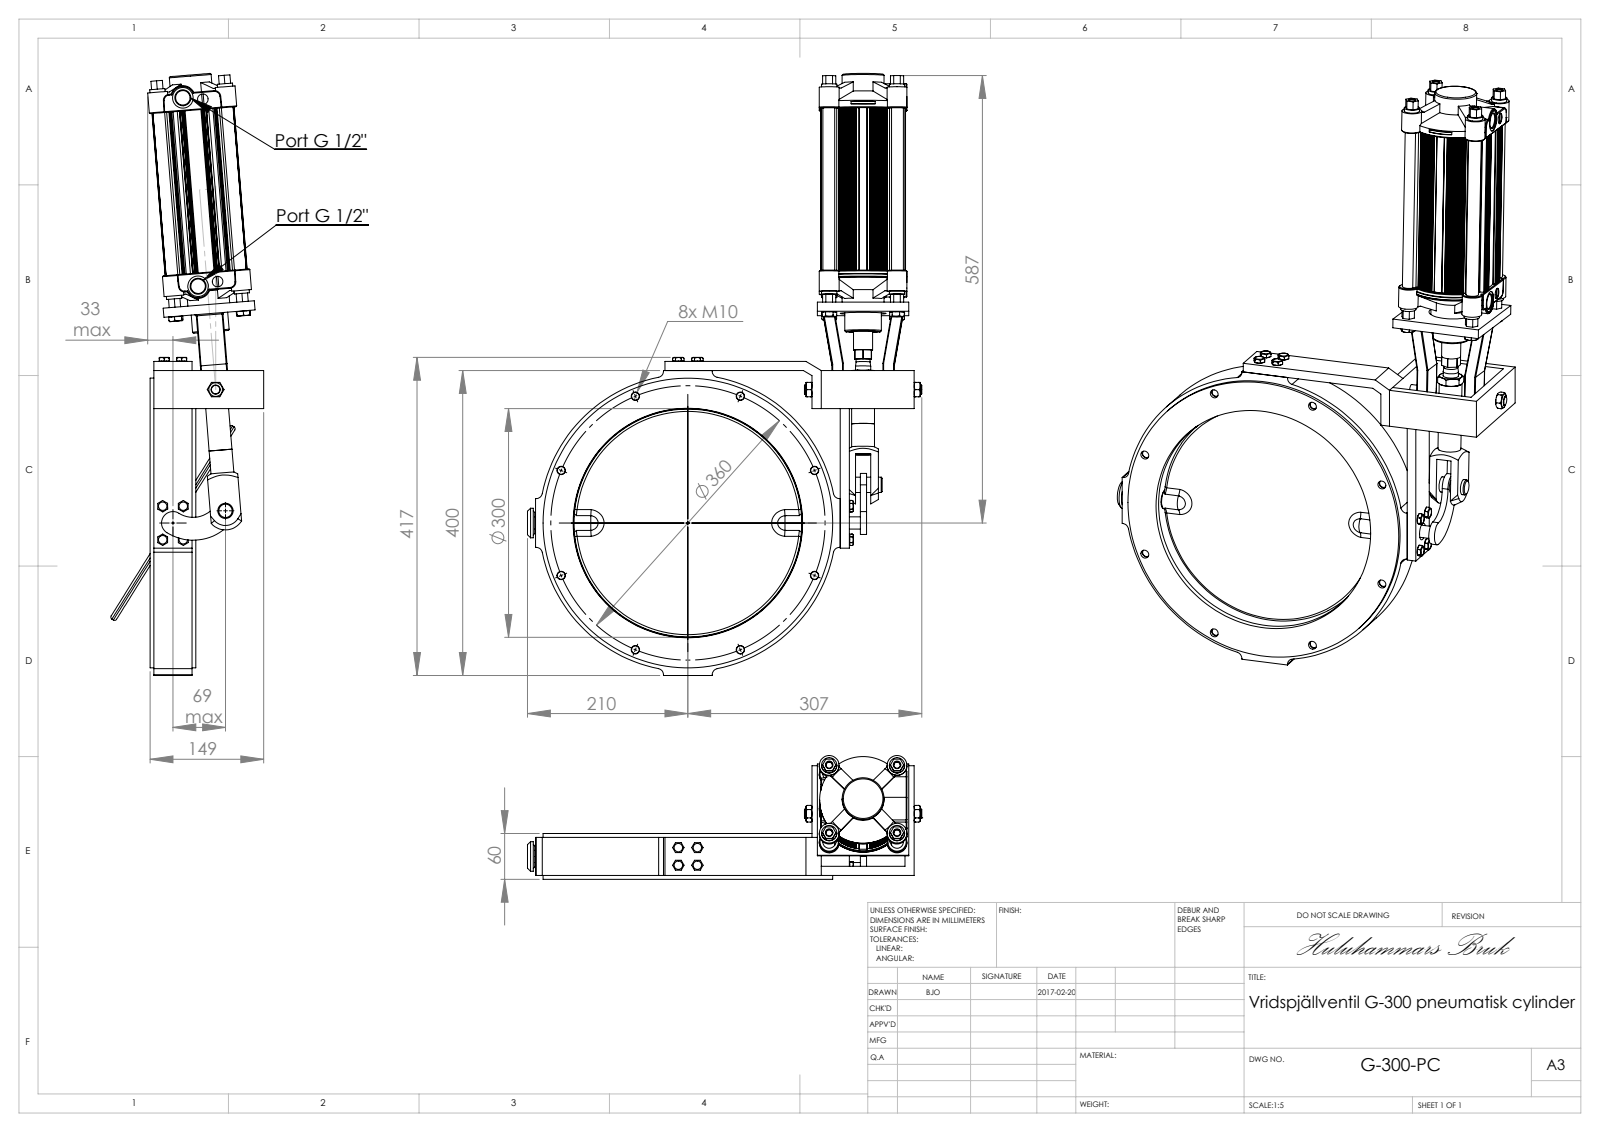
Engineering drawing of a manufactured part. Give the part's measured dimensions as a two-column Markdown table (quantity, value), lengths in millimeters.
| quantity | value |
| --- | --- |
| part name | G-300-PC; kolvstångsförlängare g300; 0822125006_Free; 0822125006_PISTON_NUT (+8 more) |
| STEP written by | SolidWorks 2011 (AUTOMOTIVE_DESIGN) |
| units | millimeters |
| bodies | 26 solids, 1156 faces (543 planar, 453 cylindrical, 160 other) |
| overall size | 789.77 × 517.45 × 162.37 |
| volume | 6 190 000 mm³ |
| surface area | 1 262 000 mm² |
| round holes (diameter × count) | 11 × 12, 8 × 8, 8.5 × 8, 10 × 8, 12 × 5, 9.4 × 4, 13.9 × 2, 19 × 2, 27 × 2, 10.5 × 1, 16 × 1, 18.5 × 1 |
| round bosses / shafts (diameter × count) | 20 × 10, 26 × 8, 13 × 8, 17 × 4, 10 × 4, 55 × 2, 25 × 2, 380 × 1 |
| partial cylindrical surfaces (radius × count) | 0.3 × 92, 1.15 × 64, 1 × 40, 2 × 30, 8 × 12, 0.2 × 8, 1.44 × 4, 5 × 4 |
| main face-to-face distances | 20.85, 29.15, 50, 5, 25.85, 34.15, 55, 8.3, 12, 60 |
| hole center spacings | 89, 62.93, 62.94, 125.87, 62.92, 125.86, 88.99, 89.01 |
